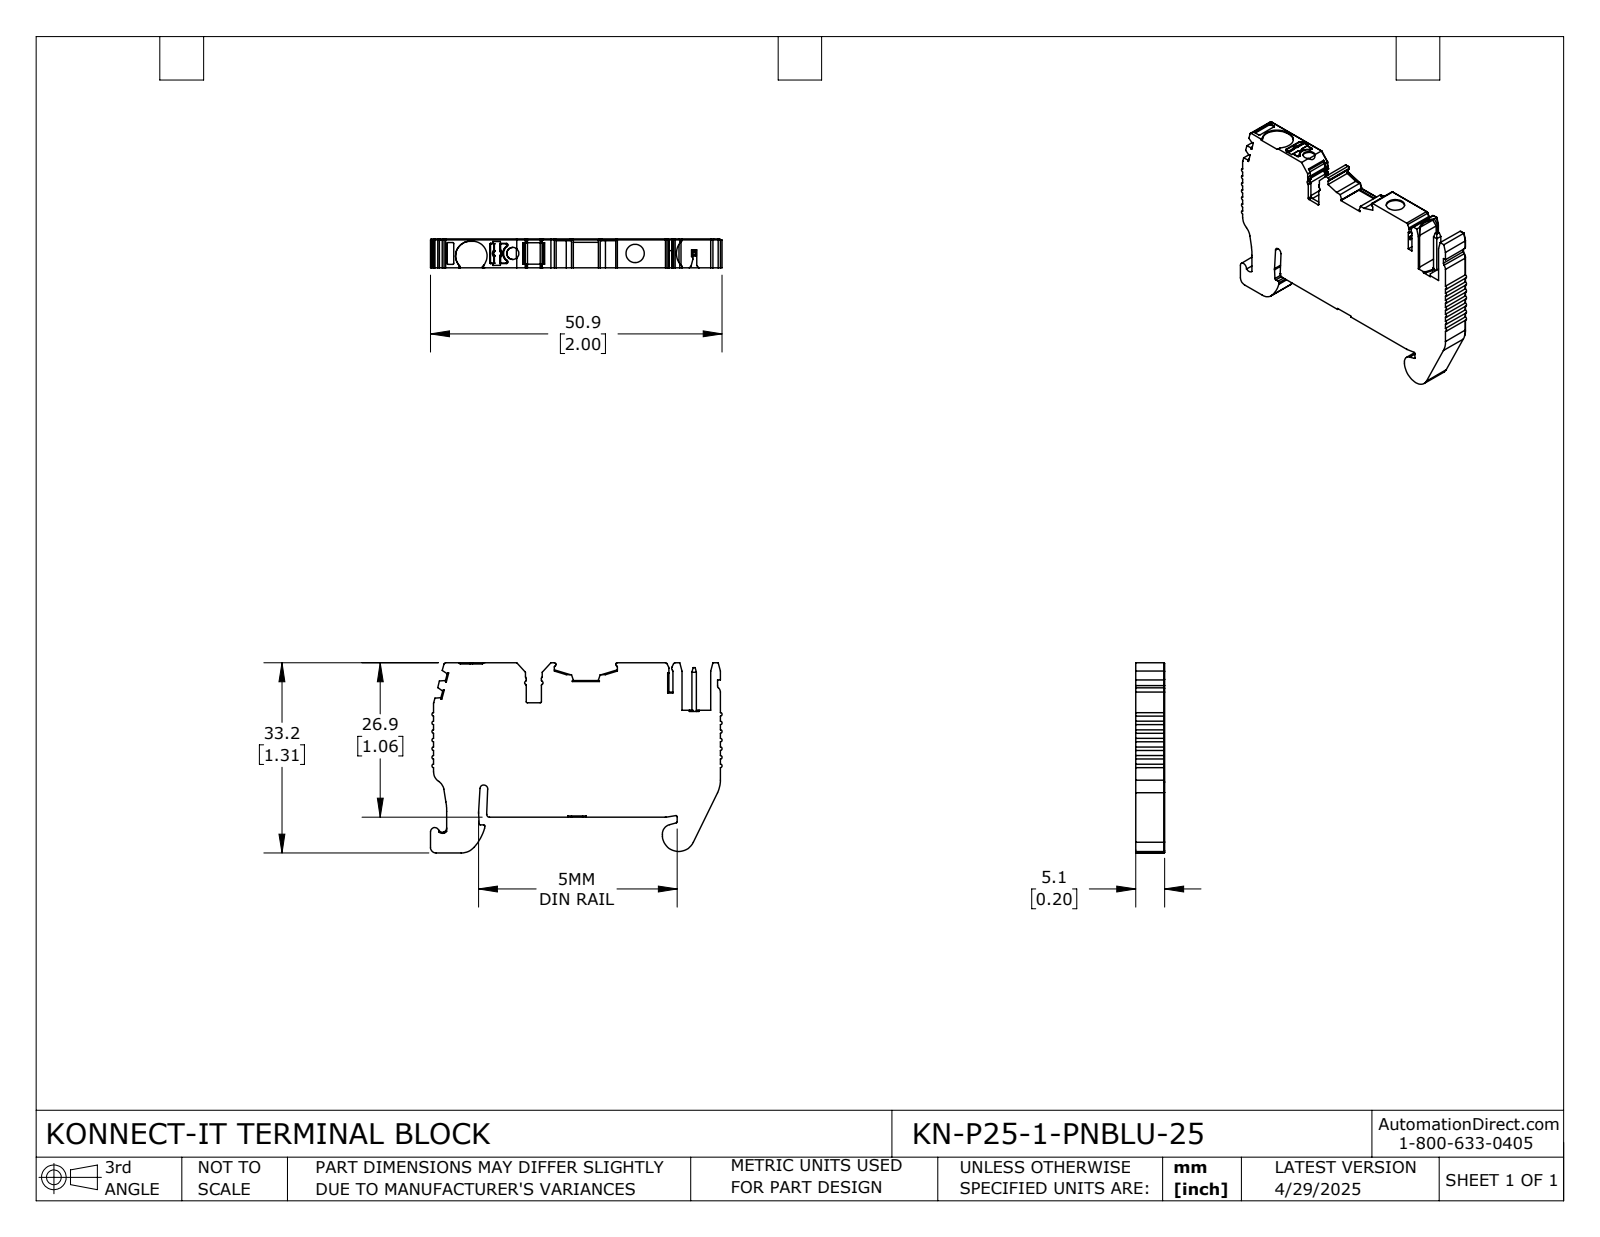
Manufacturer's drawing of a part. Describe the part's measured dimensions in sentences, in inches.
The part is named "KN-P25-1-PNBLU-25". Its 3-D file was written by "SolidWorks 2024 (CONFIG_CONTROL_DESIGN)". It is 1 solid with 461 faces: 263 planar, 179 cylindrical and 19 other. Overall it measures 2.005 by 1.307 by 0.199 inches. Its volume is 0.397 cubic inches and its surface area 6.012 square inches. Round holes: 1 of diameter 0.083, 1 of diameter 0.126. Partial cylindrical surfaces (rounded edges, fillets, slot ends): 35 of radius 0.012, 34 of radius 0.008, 13 of radius 0.02, 9 of radius 0.004, 8 of radius 0.016, 4 of radius 0.006, 3 of radius 0.024, 3 of radius 0.035. The main face-to-face distances are 0.199, 1.061, 1.053, 1.972, 1.905, 0.067, 0.981, 0.205, 1.7, 0.271. The hole center spacings are 0.841.
